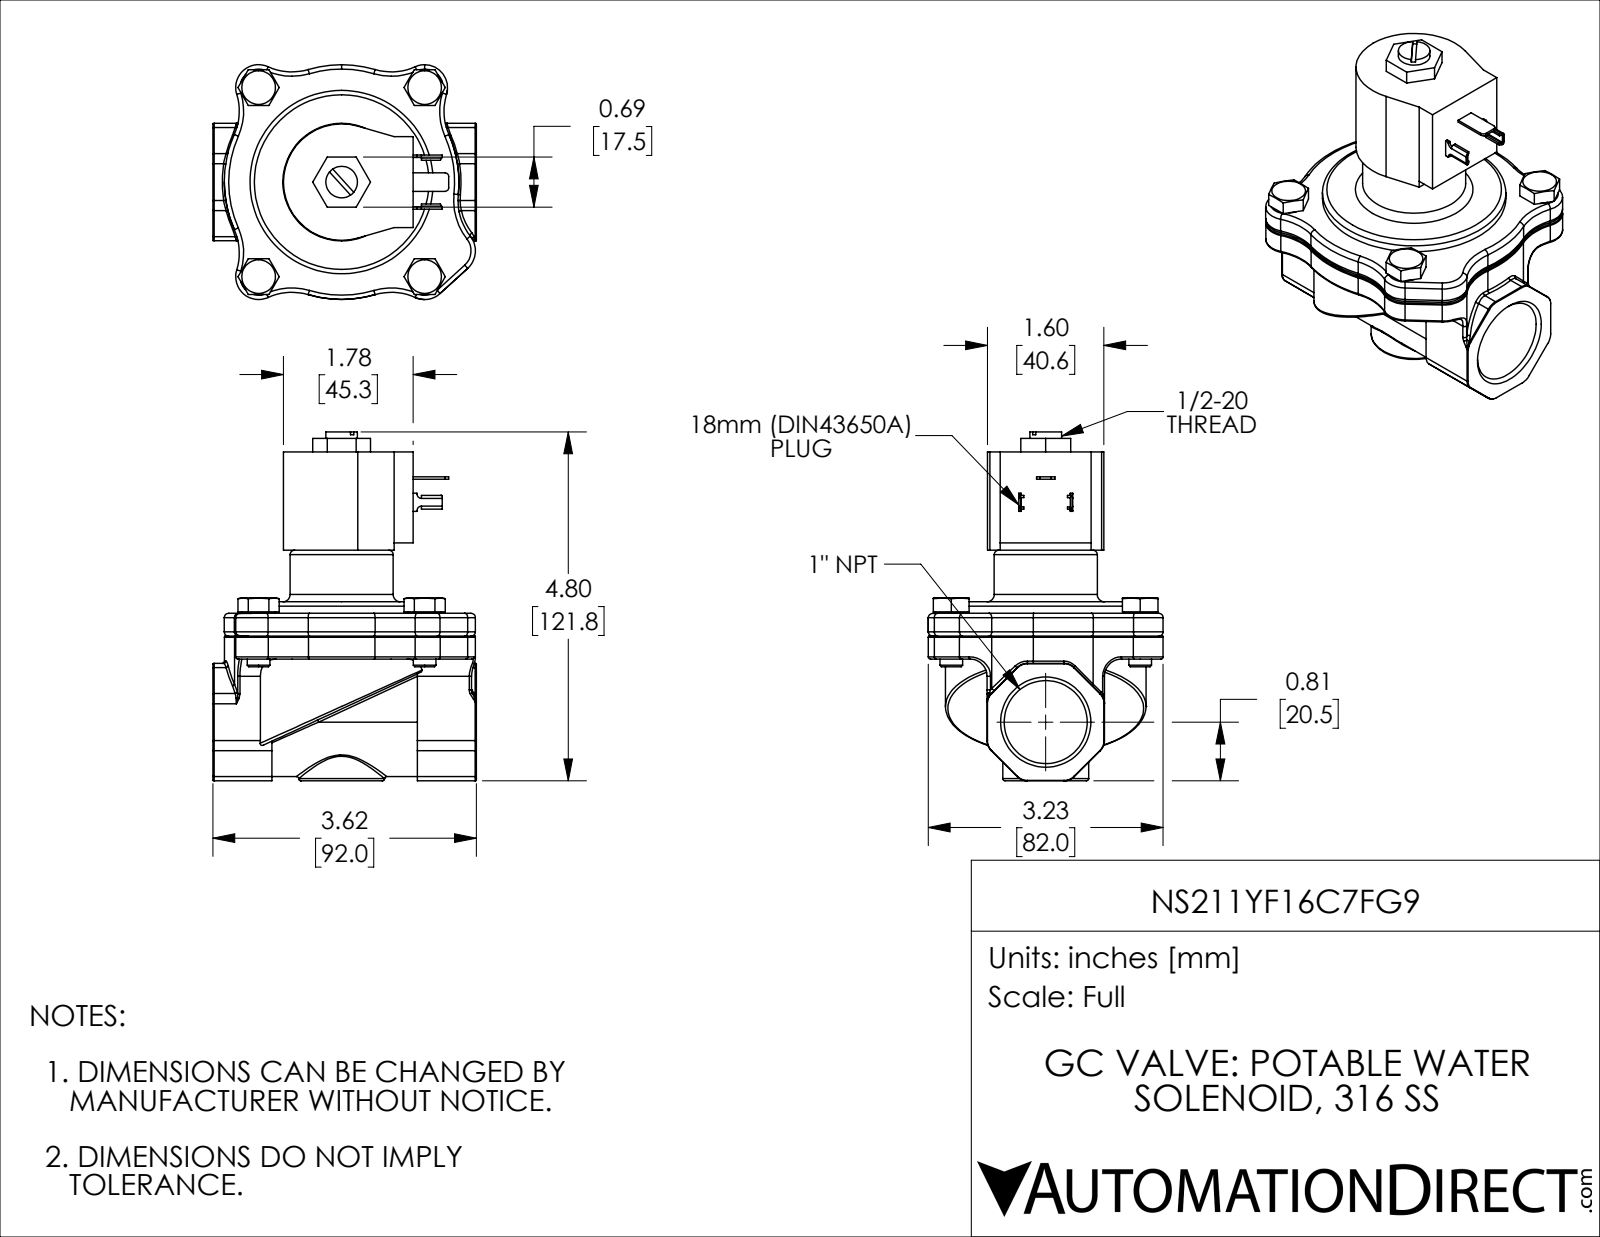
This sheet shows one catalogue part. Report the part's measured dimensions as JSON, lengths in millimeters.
{"part_name": "NS211YF16C7FG9", "step_written_by": "SolidWorks 2018 (AUTOMOTIVE_DESIGN)", "units": "millimeters", "bodies": {"solids": 9, "faces": 582, "planar": 151, "cylindrical": 223, "other": 208}, "overall_size": [121.8, 92, 82], "volume_mm3": 296800, "surface_area_mm2": 64840, "round_holes": [[6.4, 4], [8, 4], [3.2, 1], [6, 1], [11, 1], [12.8, 1], [24.1, 1], [29, 1], [76.2, 1]], "round_bosses_or_shafts": [[11.4, 4], [8, 4], [67.3, 1], [64, 1], [36, 1], [30, 1]], "partial_cylinders_radius": [[0.8, 26], [20, 16], [5, 8], [8, 6], [0.2, 4], [1, 4], [1.5, 4], [1.3, 2]], "face_to_face_distances": [0.8, 8.8, 8, 65, 64.3, 56.3, 30.8, 30, 22, 34.3], "hole_center_spacings": [66, 58, 87.9, 43.9, 43.9, 43.9, 57.8, 58]}
